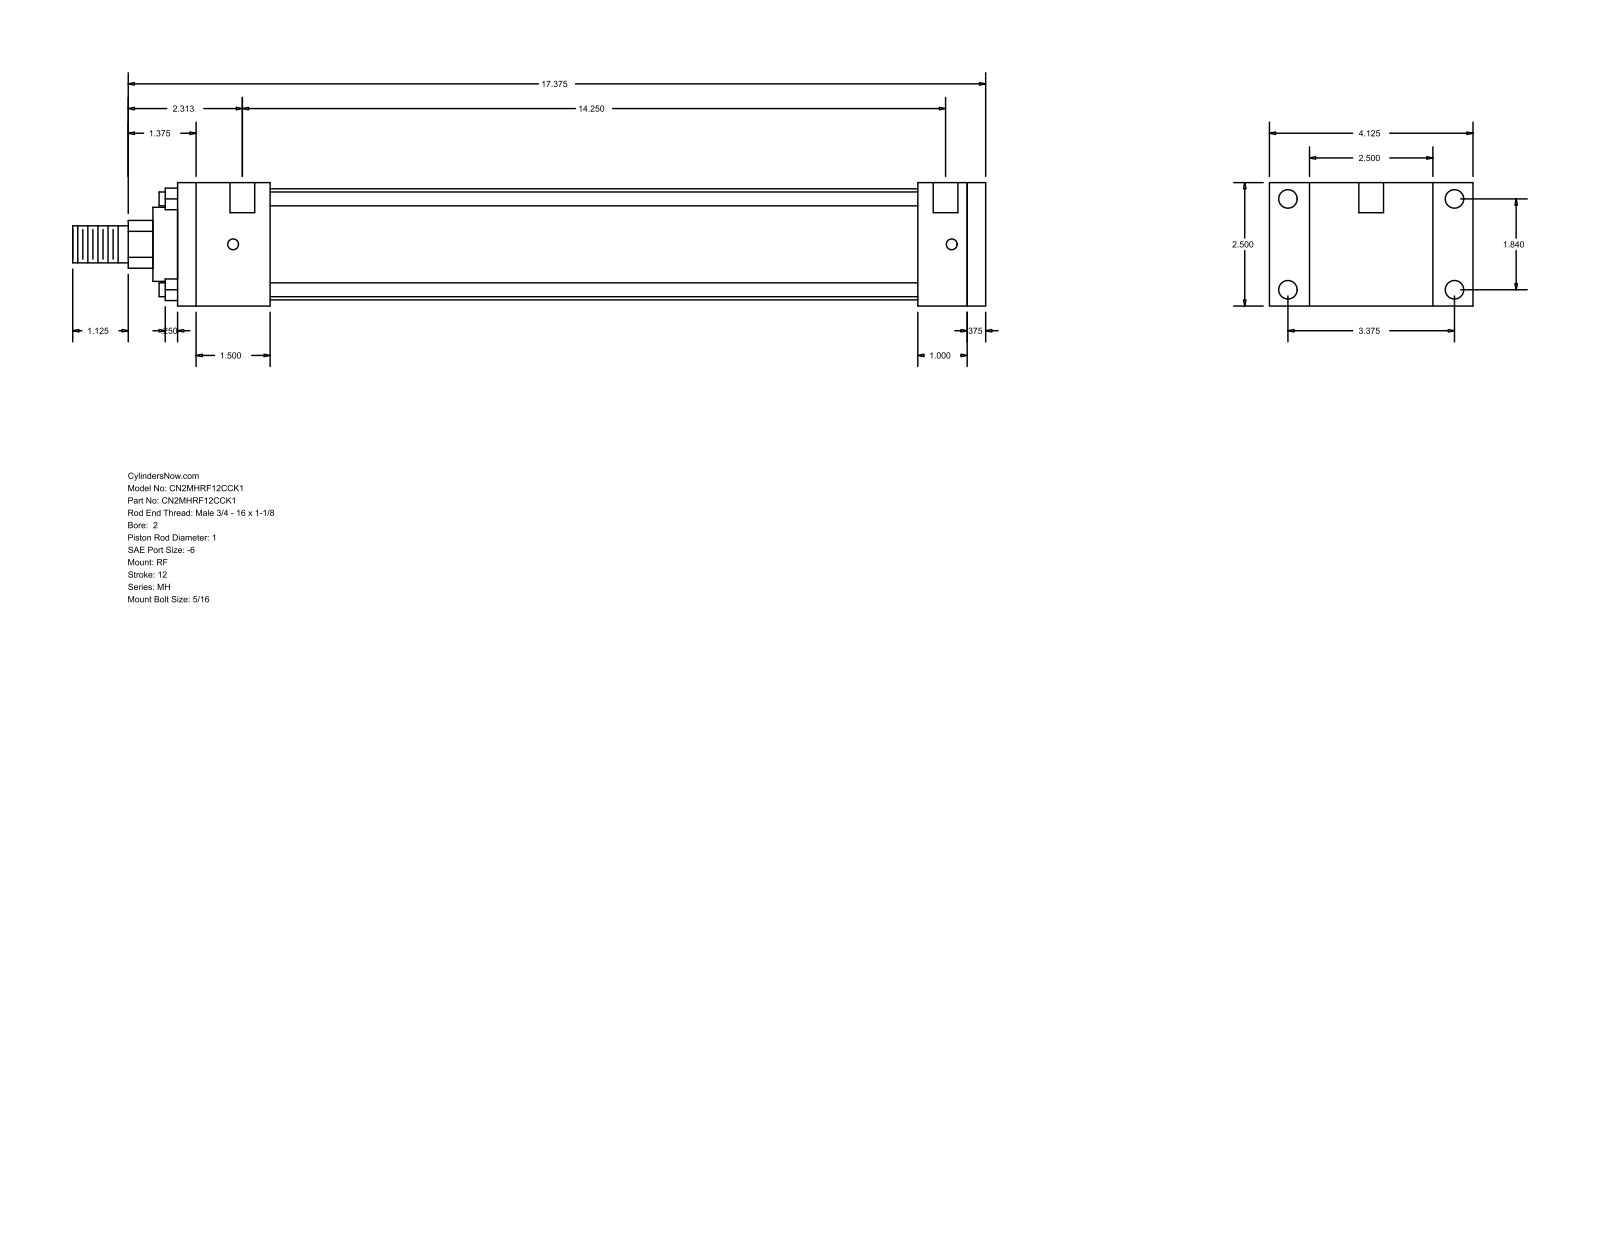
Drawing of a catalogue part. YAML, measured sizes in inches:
part_name: "MH_RF__0200_1"
step_written_by: "GSSL Pune (CONFIG_CONTROL_DESIGN)"
units: inches
bodies: {solids: 0, faces: 92, planar: 64, cylindrical: 28, other: 0}
overall_size: [18.5, 4.125, 2.5]
round_holes:
  - {diameter: 0.219, count: 4}
  - {diameter: 0.375, count: 4}
  - {diameter: 0.5, count: 2}
round_bosses_or_shafts:
  - {diameter: 0.281, count: 4}
  - {diameter: 2.25, count: 1}
  - {diameter: 1.5, count: 1}
  - {diameter: 1, count: 1}
  - {diameter: 0.75, count: 1}
partial_cylinders:
  - {radius: 0.484, count: 1}
face_to_face_distances: [2.5, 16.375, 0.375, 16, 0.813, 1, 1.875, 15, 13.125, 14.125]
hole_center_spacings: [1.84, 3.375, 3.844, 14.562, 0.125, 0.187, 14.25, 14.375]
